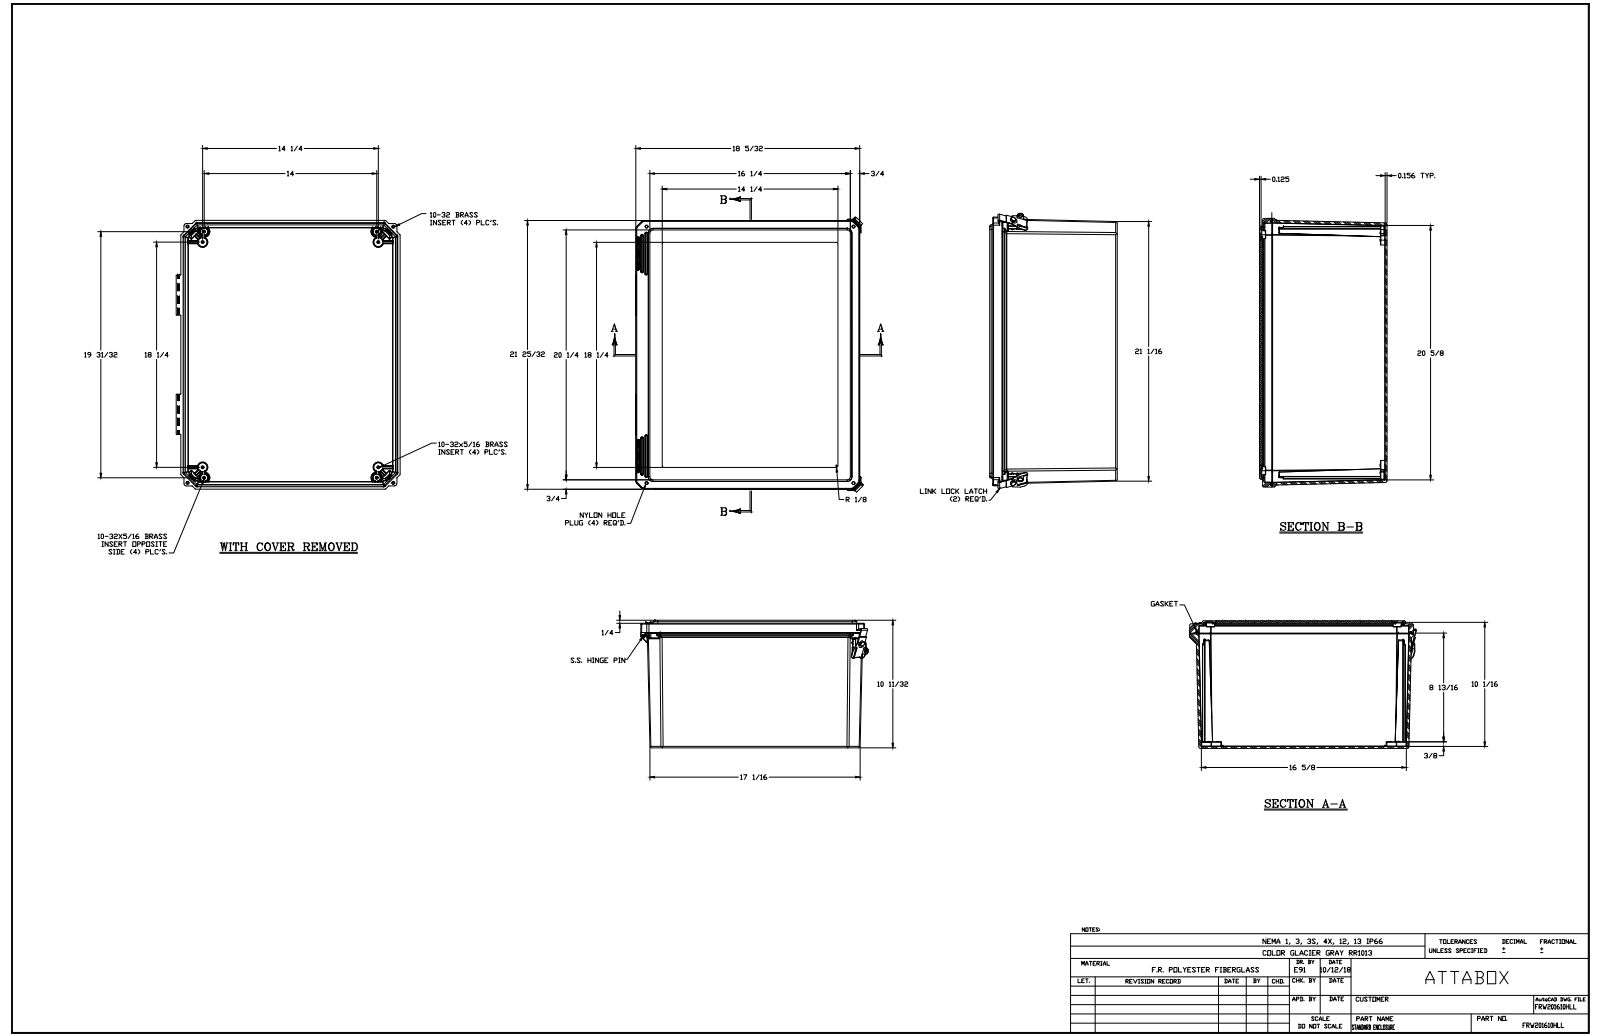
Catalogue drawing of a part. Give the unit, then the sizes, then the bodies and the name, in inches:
Units: inches
Overall size (bounding box): 22.578 × 18.561 × 10.343
Round holes (diameter × count): ⌀0.156 ×16, ⌀0.152 ×8, ⌀0.098 ×4, ⌀0.15 ×4, ⌀0.252 ×4, ⌀0.253 ×4, ⌀0.05 ×2, ⌀0.12 ×2, ⌀0.219 ×2, ⌀0.227 ×2, ⌀0.313 ×2, ⌀0.363 ×2
Round bosses / shafts (diameter × count): ⌀0.246 ×16, ⌀0.209 ×4, ⌀0.2 ×4, ⌀0.135 ×3, ⌀0.6 ×2, ⌀0.05 ×2, ⌀0.435 ×1, ⌀0.435 ×1
Partial cylindrical surfaces — rounded edges, fillets, slot ends (radius × count): R0.01 ×197, R0.005 ×88, R0.02 ×49, R0.03 ×39, R0.125 ×38, R0.039 ×28, R0.03 ×24, R0.09 ×24
Main face-to-face distances: 0.156, 0.212, 0.21, 10.119, 9.963, 10.343, 10.187, 0.225, 0.125, 10.185
Hole centre spacings: 19.56, 24.937, 0.862, 15.572, 19.103, 19.979, 20.42, 18.25
Volume: 312 in³ · Surface area: 3 270 in²
Bodies: 38 solids, 2353 faces (833 planar, 924 cylindrical, 596 other)
Part name (STEP PRODUCT): FRW201610HLL
STEP written by: SolidWorks 2018 (AUTOMOTIVE_DESIGN)
